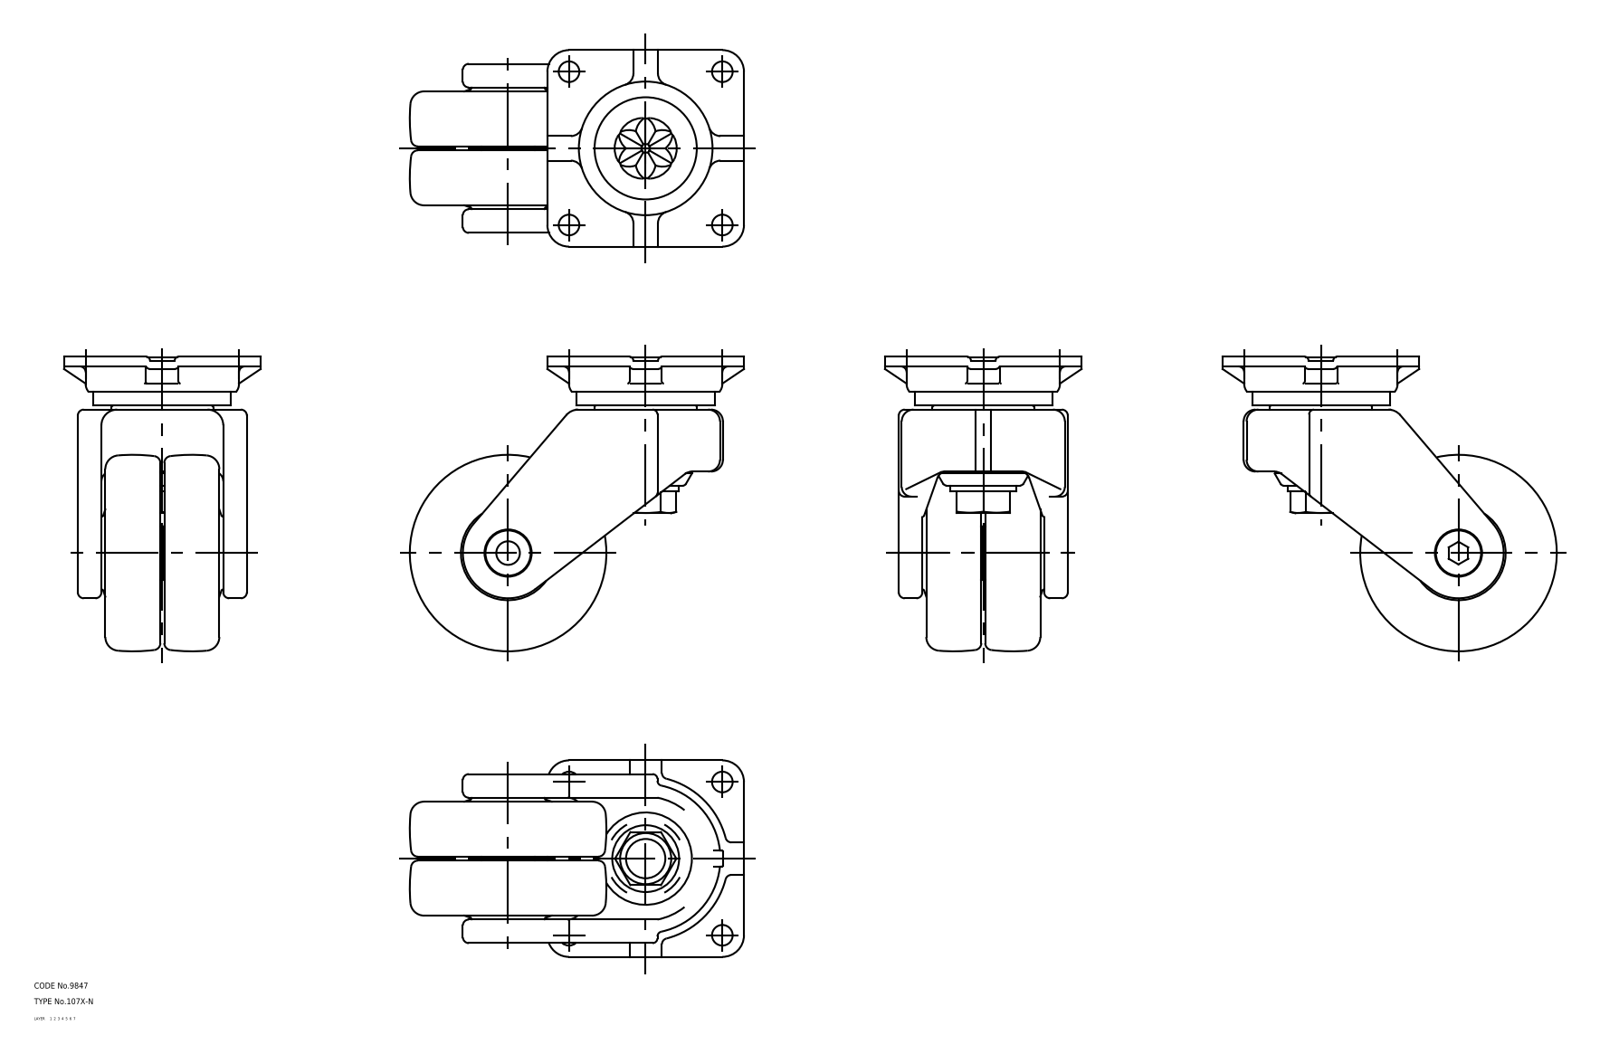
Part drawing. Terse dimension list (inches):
name: wheel; mounting plate; main shaft; axle (+1 more)
written by: CADfix (AUTOMOTIVE_DESIGN)
unit: in
bodies: 5 solids, 479 faces (0 planar, 0 cylindrical, 479 other)
size: 6.693 × 5.906 × 3.937
volume: 52.02 in³; area: 220.1 in²
